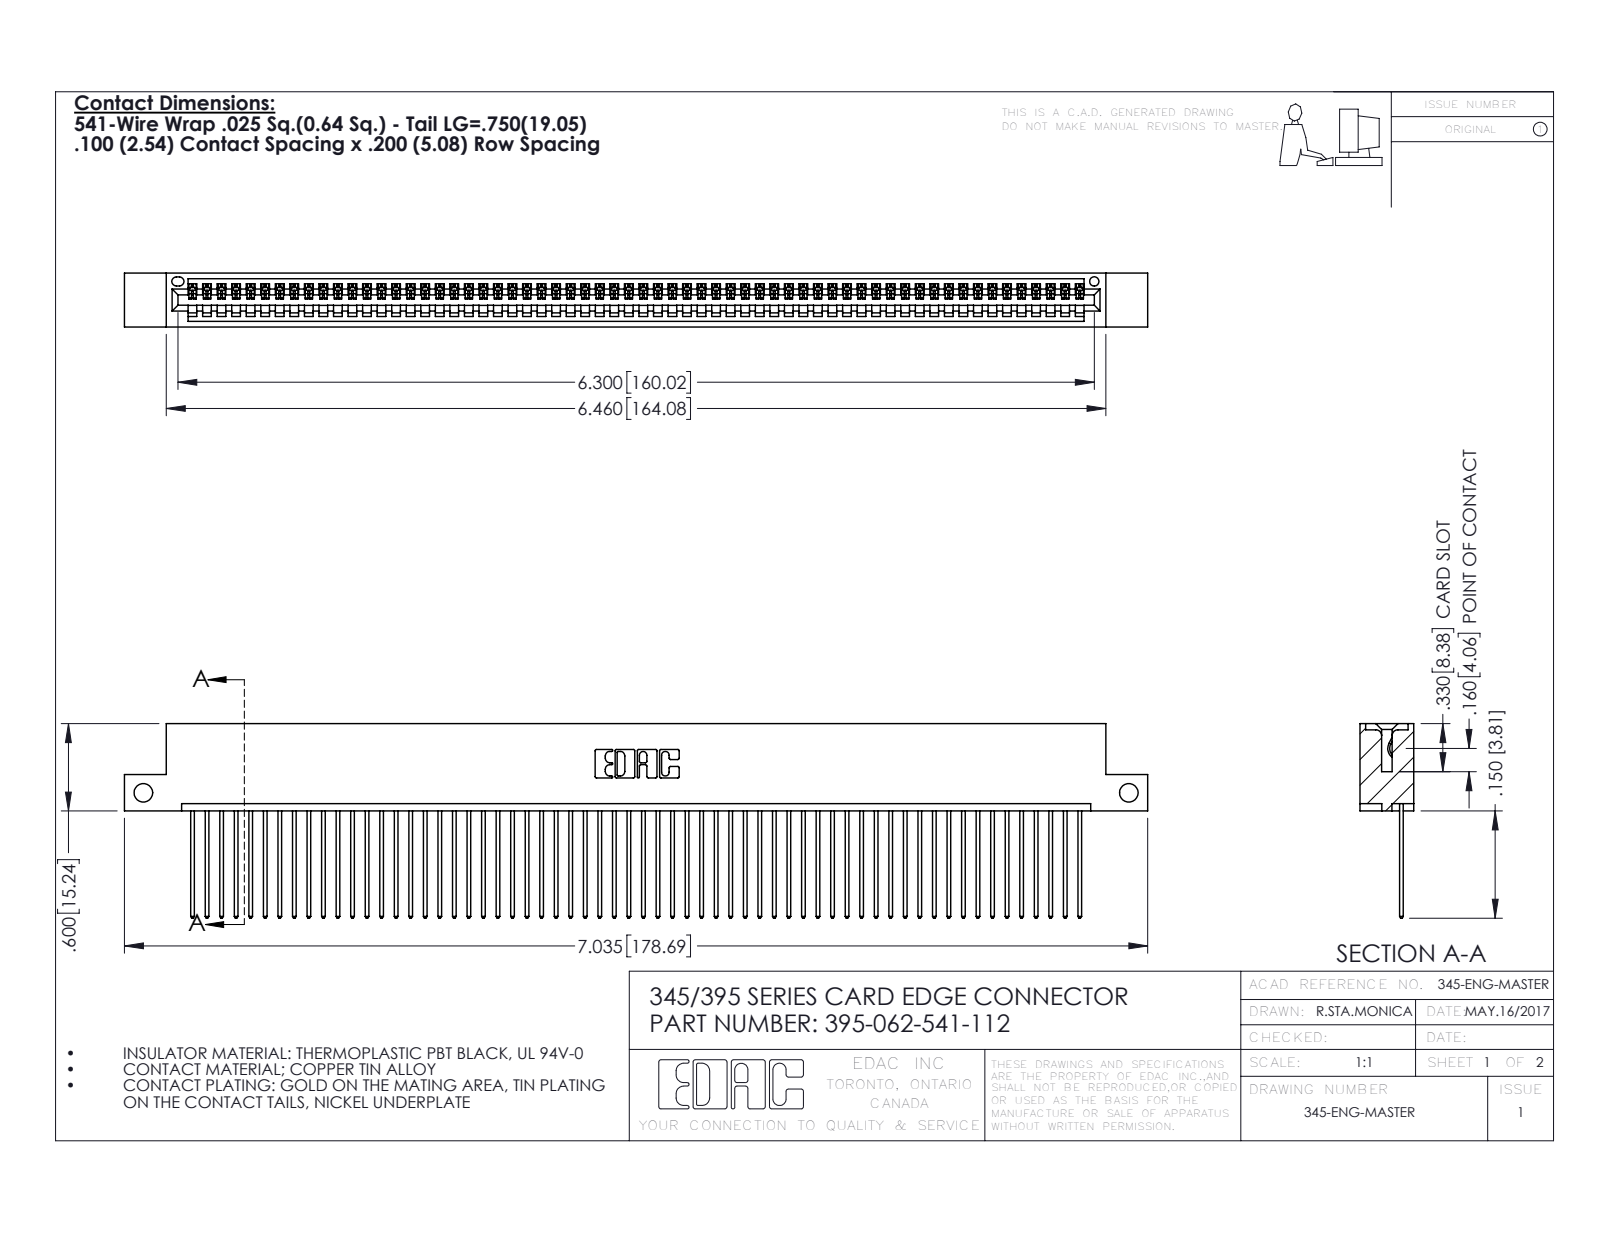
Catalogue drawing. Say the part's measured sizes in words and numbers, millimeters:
The part is named "345 Part_Flush Mounting Lugs - Side Mount; 395-062-541-112; 345-292-001_345-293-141". Its 3-D file was written by "SolidWorks 2016 (CONFIG_CONTROL_DESIGN)". It is 63 solids with 3722 faces: 2560 planar, 1162 cylindrical and 0 other. Overall it measures 178.7 by 34 by 9.4 millimeters. Its volume is 17 260 cubic millimeters and its surface area 24 260 square millimeters. Round holes: 2 of diameter 3.3, 1 of diameter 1.6. Partial cylindrical surfaces (rounded edges, fillets, slot ends): 124 of radius 0.2, 124 of radius 0.3, 22 of radius 0.3, 6 of radius 0.2, 6 of radius 0.8, 3 of radius 0.7, 2 of radius 0.8, 2 of radius 1. The main face-to-face distances are 1.8, 7.6, 2.5, 6.9, 0.6, 9.4, 5.1, 5.7, 3.8, 1.8. The hole center spacings are 172.1.
